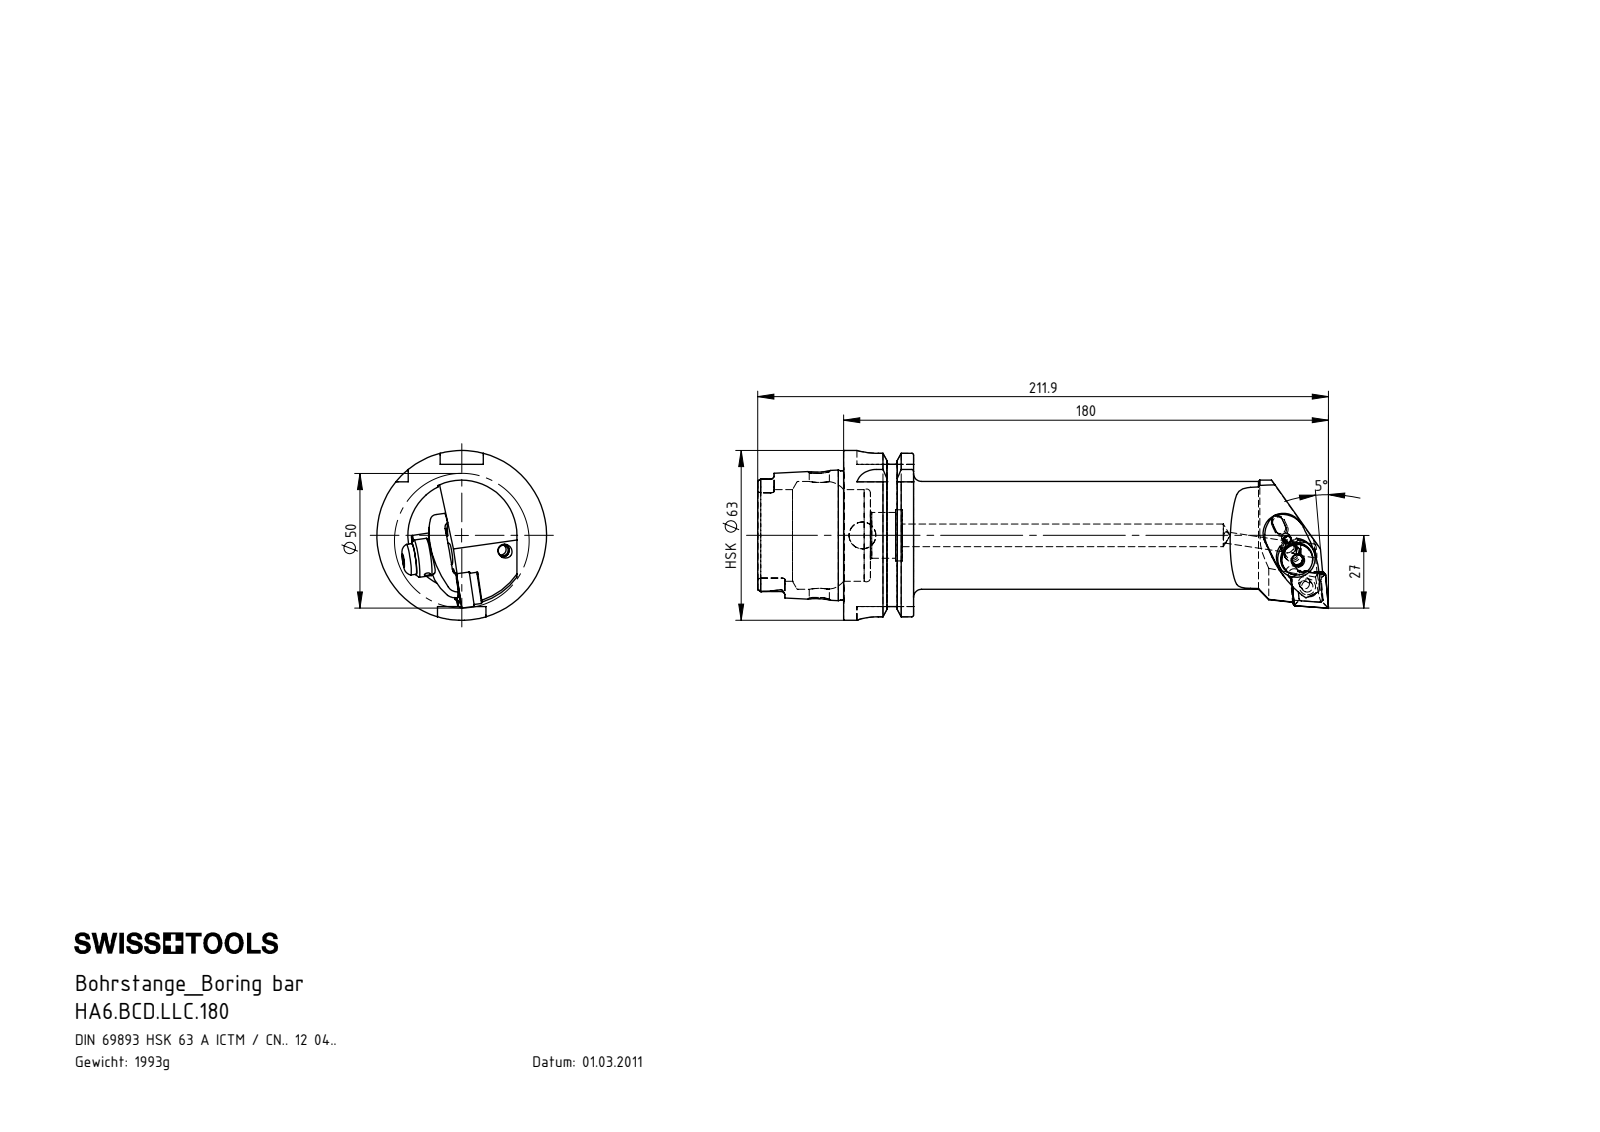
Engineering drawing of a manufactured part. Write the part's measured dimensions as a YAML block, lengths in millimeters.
part_name: "HA6-BCD.LLC.180; KVT_MB_600_050; WCC-ER5.102.005_A; CNMG120404 (+7 more)"
step_written_by: "SolidWorks 2012 (CONFIG_CONTROL_DESIGN)"
units: millimeters
bodies: {solids: 11, faces: 463, planar: 123, cylindrical: 153, other: 187}
overall_size: [211.9, 63, 63]
volume: 254282
surface_area: 49504
round_holes:
  - {diameter: 2, count: 3}
  - {diameter: 4.2, count: 3}
  - {diameter: 5, count: 2}
  - {diameter: 7, count: 2}
  - {diameter: 2.4, count: 1}
  - {diameter: 3, count: 1}
  - {diameter: 4, count: 1}
  - {diameter: 5.16, count: 1}
  - {diameter: 6.2, count: 1}
  - {diameter: 6.4, count: 1}
  - {diameter: 7.5, count: 1}
  - {diameter: 8.4, count: 1}
round_bosses_or_shafts:
  - {diameter: 5, count: 2}
  - {diameter: 3, count: 2}
  - {diameter: 63, count: 1}
  - {diameter: 54.95, count: 1}
  - {diameter: 47.94, count: 1}
  - {diameter: 14, count: 1}
  - {diameter: 11.5, count: 1}
  - {diameter: 7, count: 1}
partial_cylinders:
  - {radius: 0.39, count: 6}
  - {radius: 0.69, count: 6}
  - {radius: 1.4, count: 6}
  - {radius: 0.4, count: 4}
  - {radius: 1, count: 4}
  - {radius: 8, count: 4}
  - {radius: 1.5, count: 3}
  - {radius: 3, count: 3}
face_to_face_distances: [25.95, 16, 9.95, 31.9, 41.85, 57.85, 52.8, 21.8, 11.85, 4.49]
hole_center_spacings: [7.71, 8, 14.94, 7.53, 7.99, 8.01, 8.2, 8.21]
